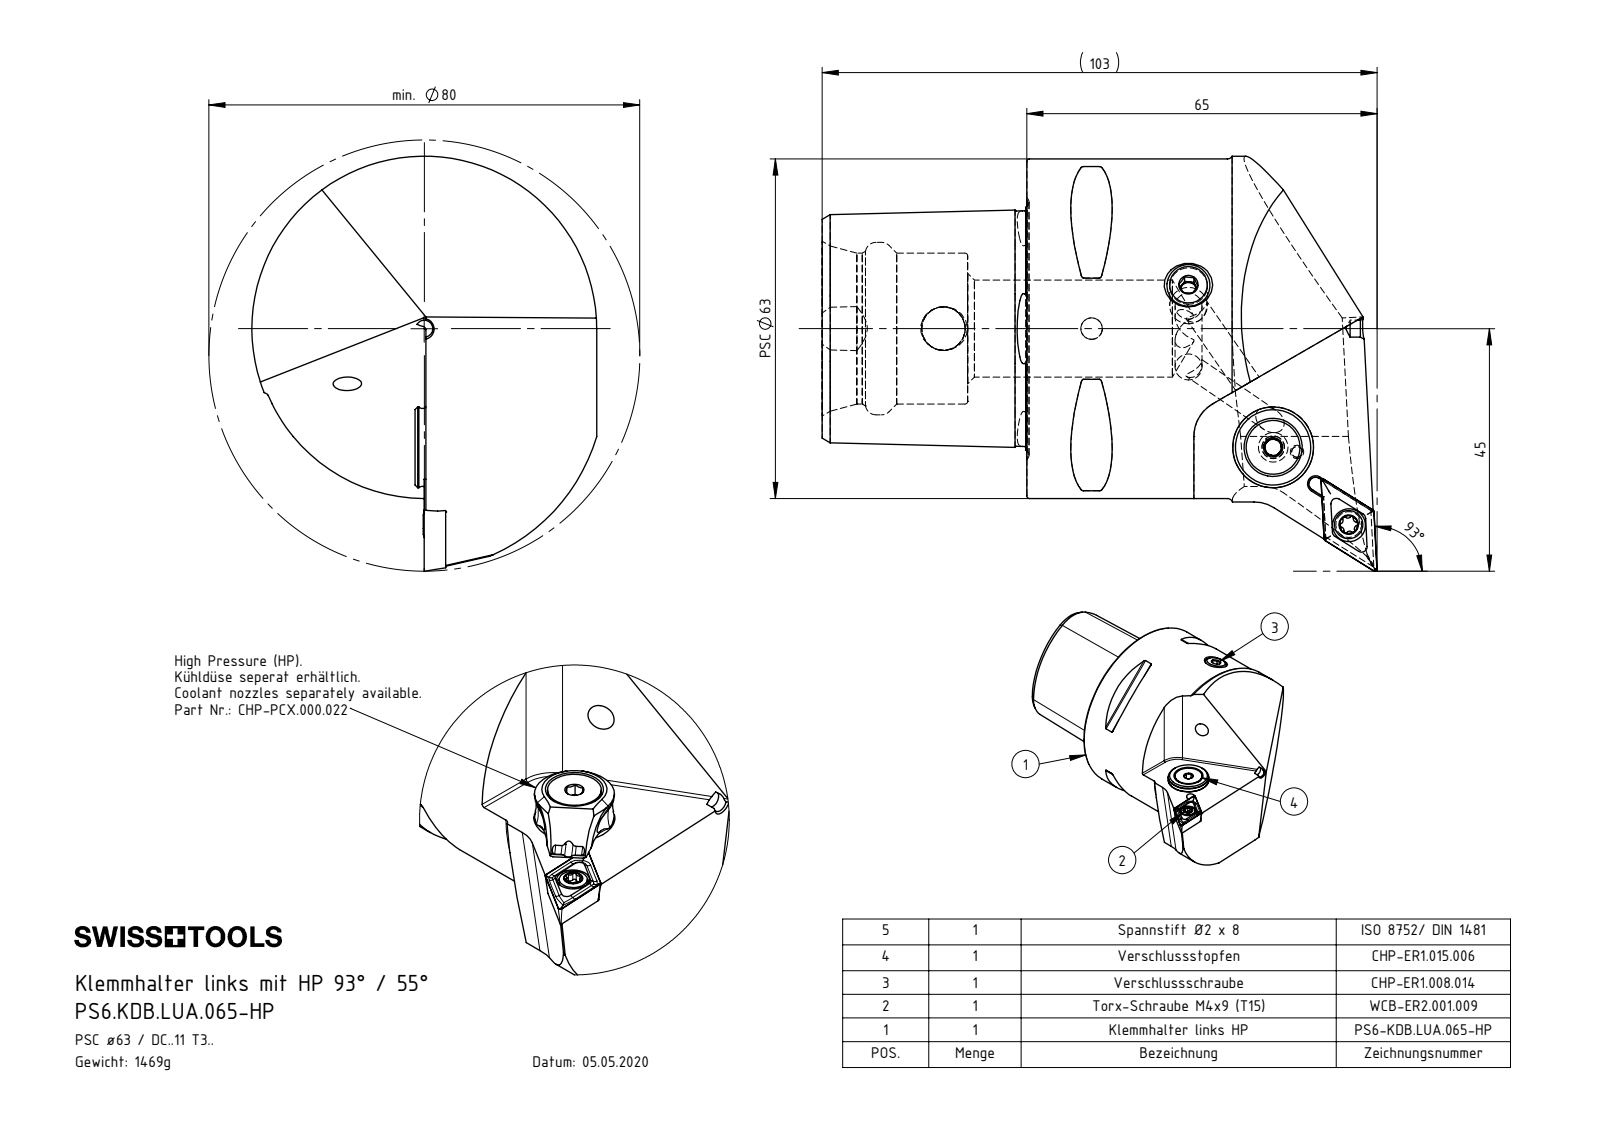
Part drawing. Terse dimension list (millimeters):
name: CHP-ER1.015.006_A; CHP-ER1.008.014_A; DCMT11T304; DIN 7991 - M5x15 (+6 more)
written by: SolidWorks 2017 (AUTOMOTIVE_DESIGN)
unit: mm
bodies: 8 solids, 383 faces (91 planar, 101 cylindrical, 191 other)
size: 103 × 77.01 × 64
volume: 187 205 mm³; area: 32 192 mm²
holes: 2× ⌀4.2, 2× ⌀5, 1× ⌀1.2, 1× ⌀2, 1× ⌀2.5, 1× ⌀3, 1× ⌀3.3, 1× ⌀4, 1× ⌀4.4, 1× ⌀5.2, 1× ⌀6.1, 1× ⌀7
bosses: 1× ⌀63, 1× ⌀15, 1× ⌀13.4, 1× ⌀10, 1× ⌀8, 1× ⌀5.5, 1× ⌀5.25, 1× ⌀5
rounds: 10× R0.5, 6× R0.34, 6× R0.59, 2× R7, 1× R1.25, 1× R1.57, 1× R6, 1× R32
face distances: 38, 31.7, 24.88, 27.2, 4.5, 27, 11, 69, 42, 31
hole spacings: 4.49, 16.55, 16.67, 20.05, 20.17, 27.5, 40.27, 44.47
